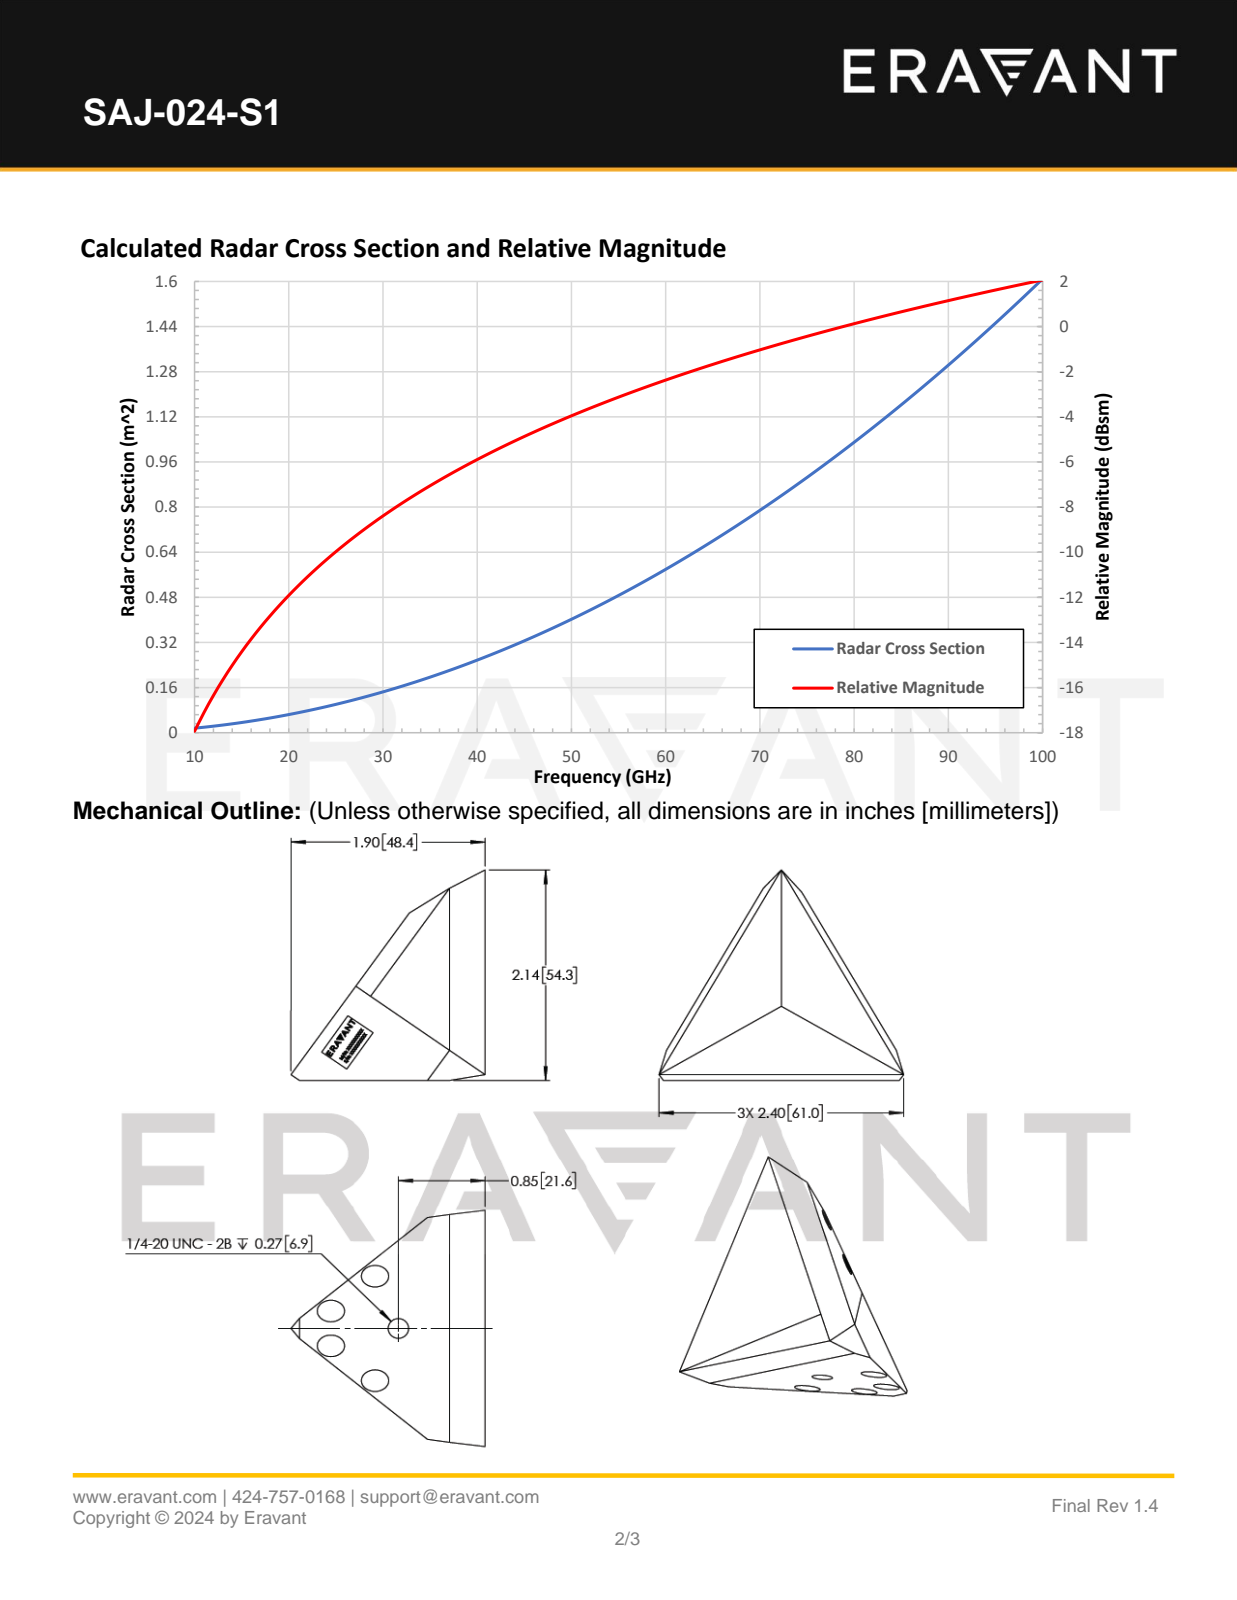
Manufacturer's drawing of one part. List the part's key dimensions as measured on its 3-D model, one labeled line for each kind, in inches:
Part name (STEP PRODUCT): SAJ-024-S1
STEP written by: SolidWorks 2016 (CONFIG_CONTROL_DESIGN)
Units: inches
Bodies: 3 solids, 23 faces (19 planar, 2 cylindrical, 2 other)
Overall size (bounding box): 2.797 × 2.4 × 1.554
Volume: 1.664 in³ · Surface area: 16.46 in²
Round holes (diameter × count): ⌀0.201 ×1
Main face-to-face distances: 0.25, 1.1
